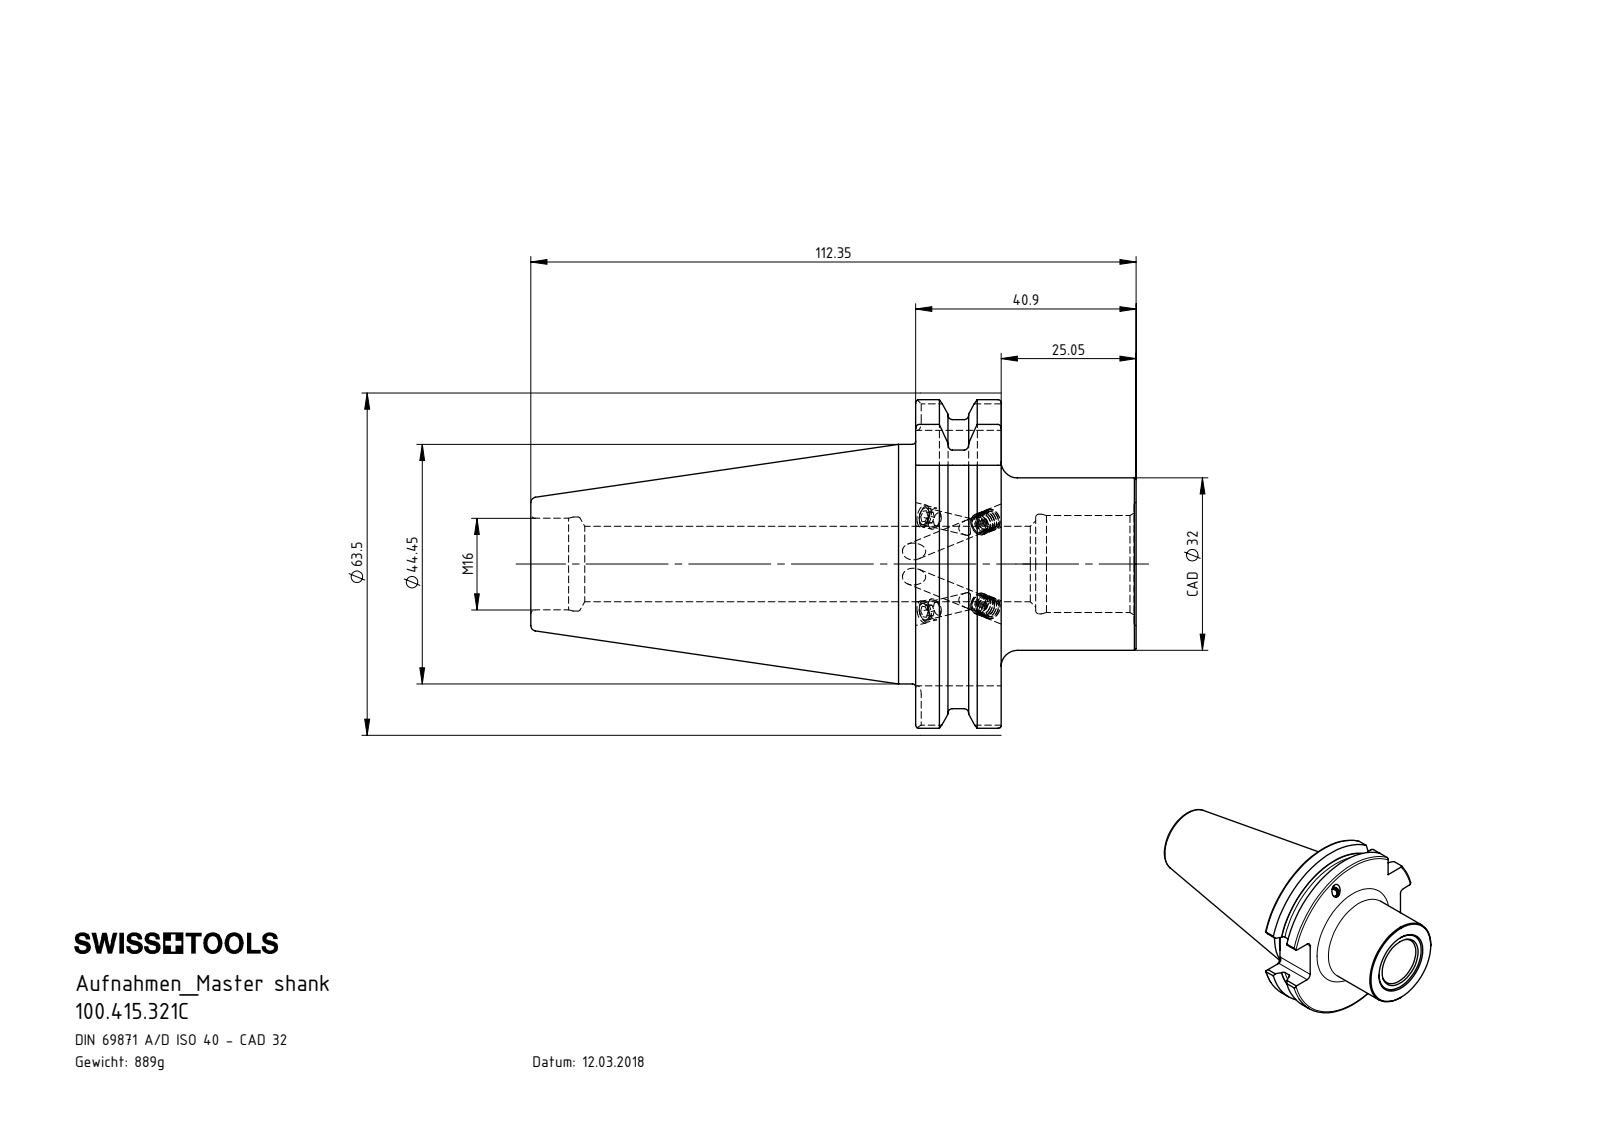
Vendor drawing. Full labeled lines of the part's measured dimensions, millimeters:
Part name (STEP PRODUCT): SB4-CA3.K01.044_B; 100.415.321C; KVT_MB_600_040; ISO 4026 - M4 x 3_PreviewCfg
STEP written by: SolidWorks 2017 (CONFIG_CONTROL_DESIGN)
Units: millimetres
Bodies: 7 solids, 236 faces (55 planar, 63 cylindrical, 118 other)
Overall size (bounding box): 112.35 × 63.5 × 60.94
Volume: 113 298 mm³ · Surface area: 24 848 mm²
Round holes (diameter × count): ⌀3 ×2, ⌀3.2 ×2, ⌀3.3 ×2, ⌀4 ×2, ⌀4.2 ×2, ⌀14 ×1, ⌀17 ×1, ⌀17.45 ×1, ⌀18 ×1, ⌀18.5 ×1
Round bosses / shafts (diameter × count): ⌀4 ×4, ⌀44.45 ×1, ⌀32 ×1
Partial cylindrical surfaces — rounded edges, fillets, slot ends (radius × count): R1.6 ×8, R28 ×1, R31.75 ×1
Main face-to-face distances: 15.85, 40.9, 25.05, 47.4, 71.45, 87.3, 112.35, 111.95, 40.5, 24.65
